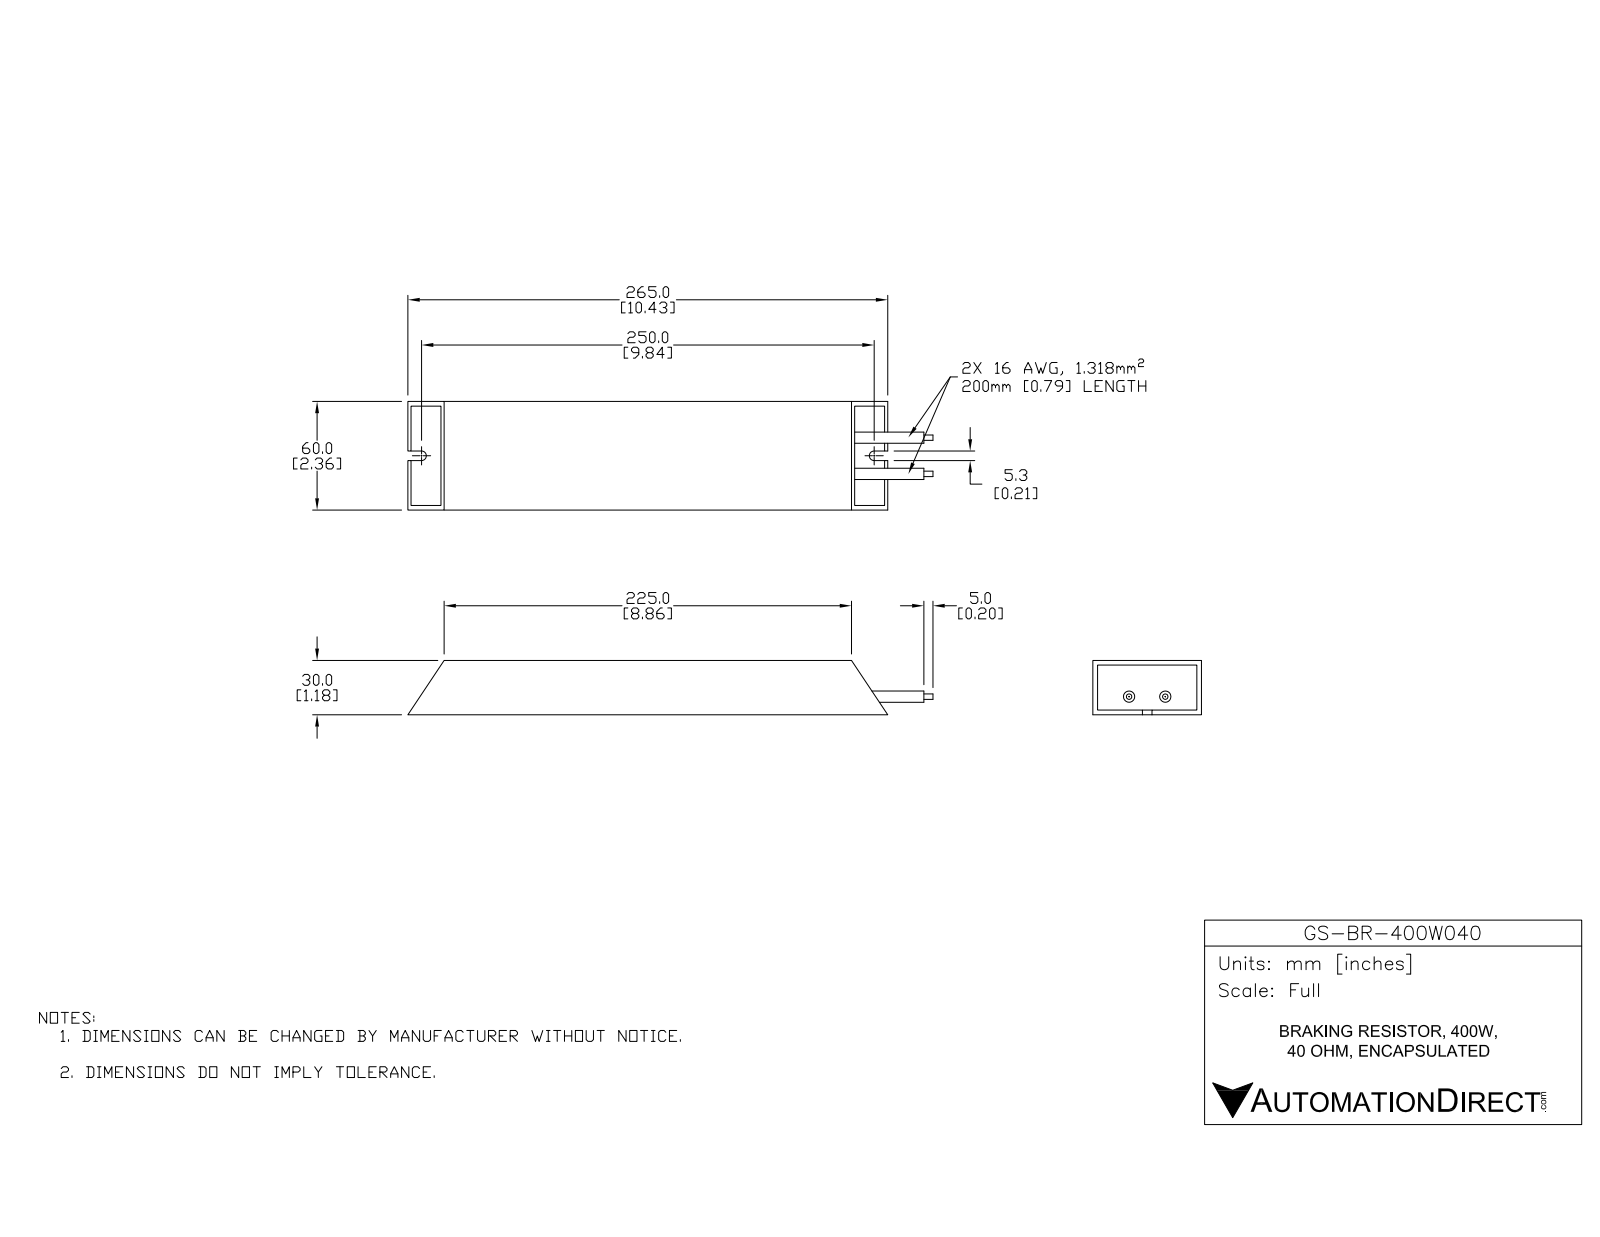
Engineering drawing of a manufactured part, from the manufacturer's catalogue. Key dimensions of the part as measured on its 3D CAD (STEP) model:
Part name (STEP PRODUCT): GS-BR-400W040
STEP written by: SolidWorks 2015 (AUTOMOTIVE_DESIGN)
Units: inches
Bodies: 1 solid, 34 faces (24 planar, 10 cylindrical, 0 other)
Overall size (bounding box): 11.417 × 2.362 × 1.181
Volume: 25.39 in³ · Surface area: 81.54 in²
Round bosses / shafts (diameter × count): ⌀0.244 ×2, ⌀0.118 ×2
Partial cylindrical surfaces — rounded edges, fillets, slot ends (radius × count): R0.104 ×2
Main face-to-face distances: 1.181, 2.362, 0.102, 1.079, 8.858, 2.26, 2.157, 0.976, 1.077, 1.285
